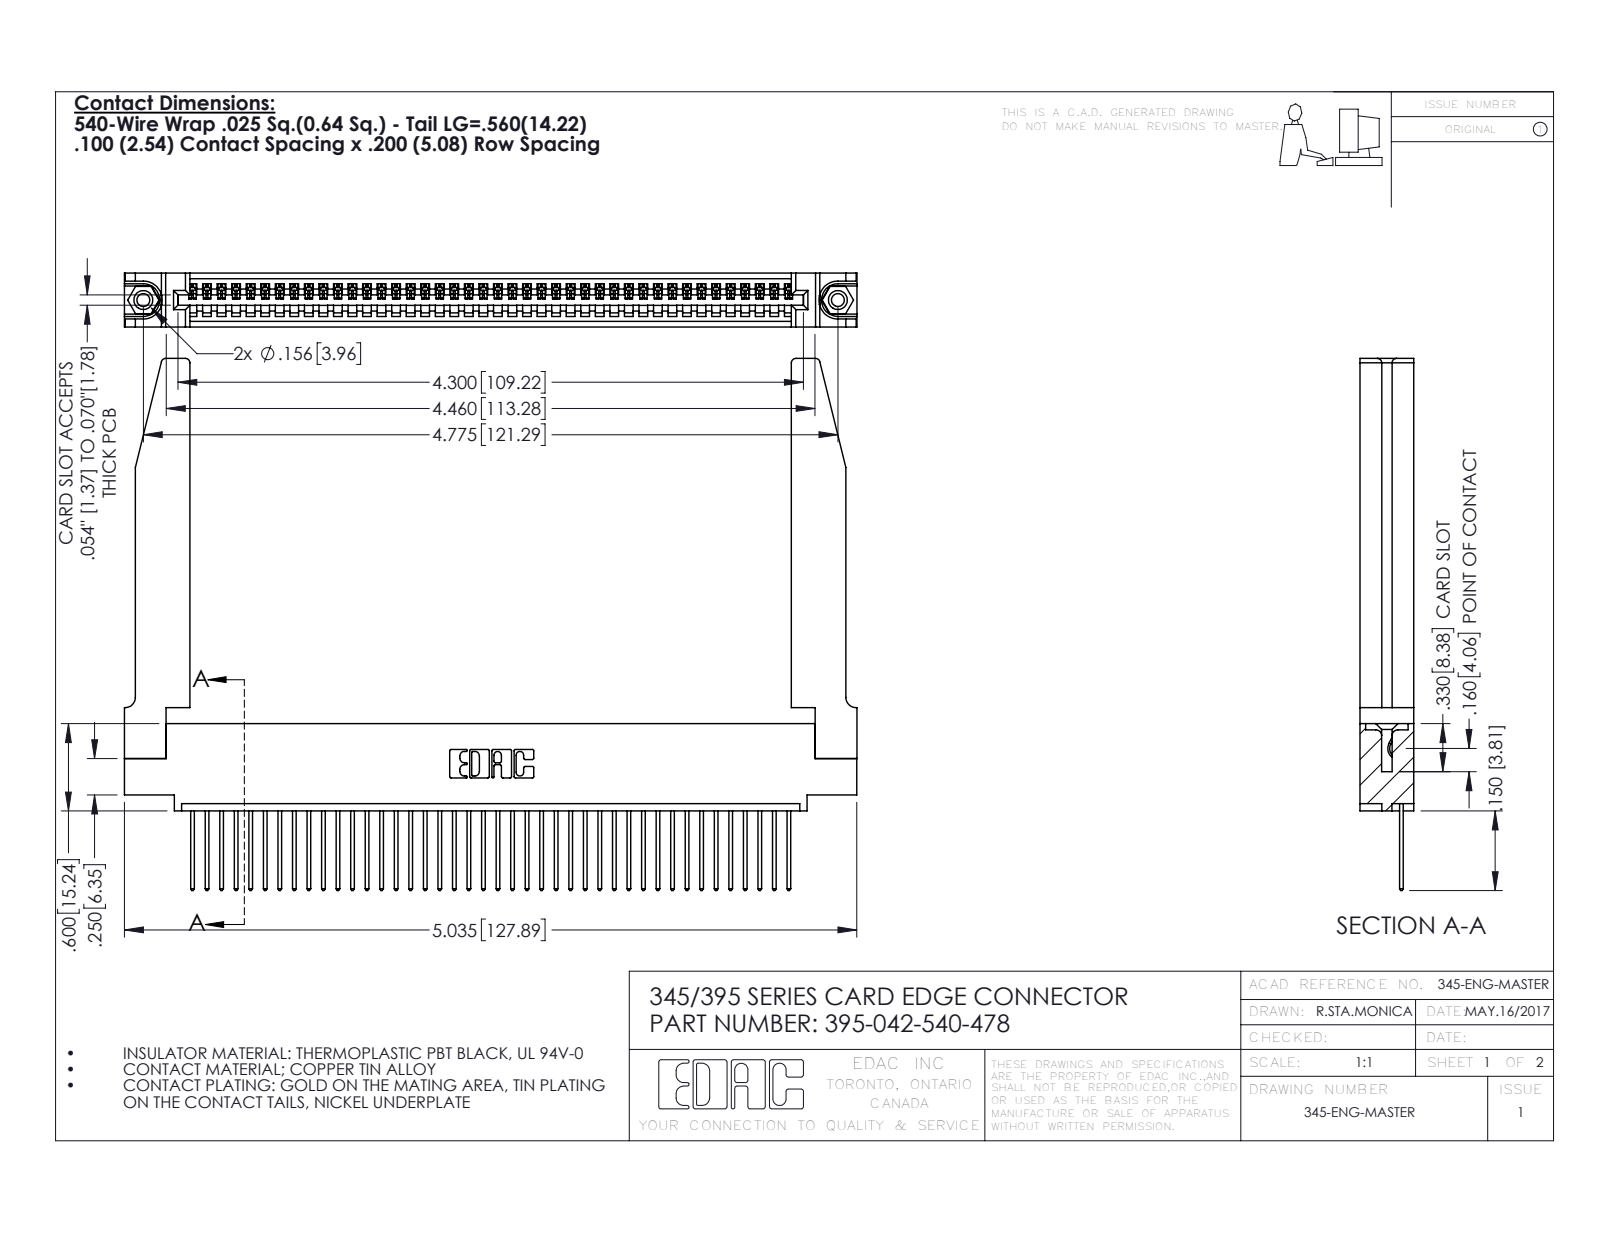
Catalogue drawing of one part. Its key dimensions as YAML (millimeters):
part_name: "345-250-001_345-250-001-102; 345-292-001_345-293-140; 345 Part_0.110 Offset - 0.156 Dia-TH; 395-042-540-478 (+1 more)"
step_written_by: "SolidWorks 2016 (CONFIG_CONTROL_DESIGN)"
units: millimeters
bodies: {solids: 47, faces: 2800, planar: 1906, cylindrical: 842, other: 52}
overall_size: [127.9, 92.9, 9.4]
volume: 19910
surface_area: 23460
round_holes:
  - {diameter: 2.3, count: 2}
  - {diameter: 3.2, count: 2}
  - {diameter: 4, count: 2}
  - {diameter: 1.6, count: 1}
round_bosses_or_shafts:
  - {diameter: 3.9, count: 2}
partial_cylinders:
  - {radius: 0.2, count: 84}
  - {radius: 0.3, count: 84}
  - {radius: 0.3, count: 22}
  - {radius: 0.8, count: 8}
  - {radius: 0.2, count: 6}
  - {radius: 0.8, count: 6}
  - {radius: 0.7, count: 3}
  - {radius: 0.8, count: 2}
face_to_face_distances: [9.4, 1.8, 7.6, 2.5, 6.9, 0.6, 5.1, 5.7, 3.8, 3.8]
hole_center_spacings: [6.9, 115.3, 121.3]
